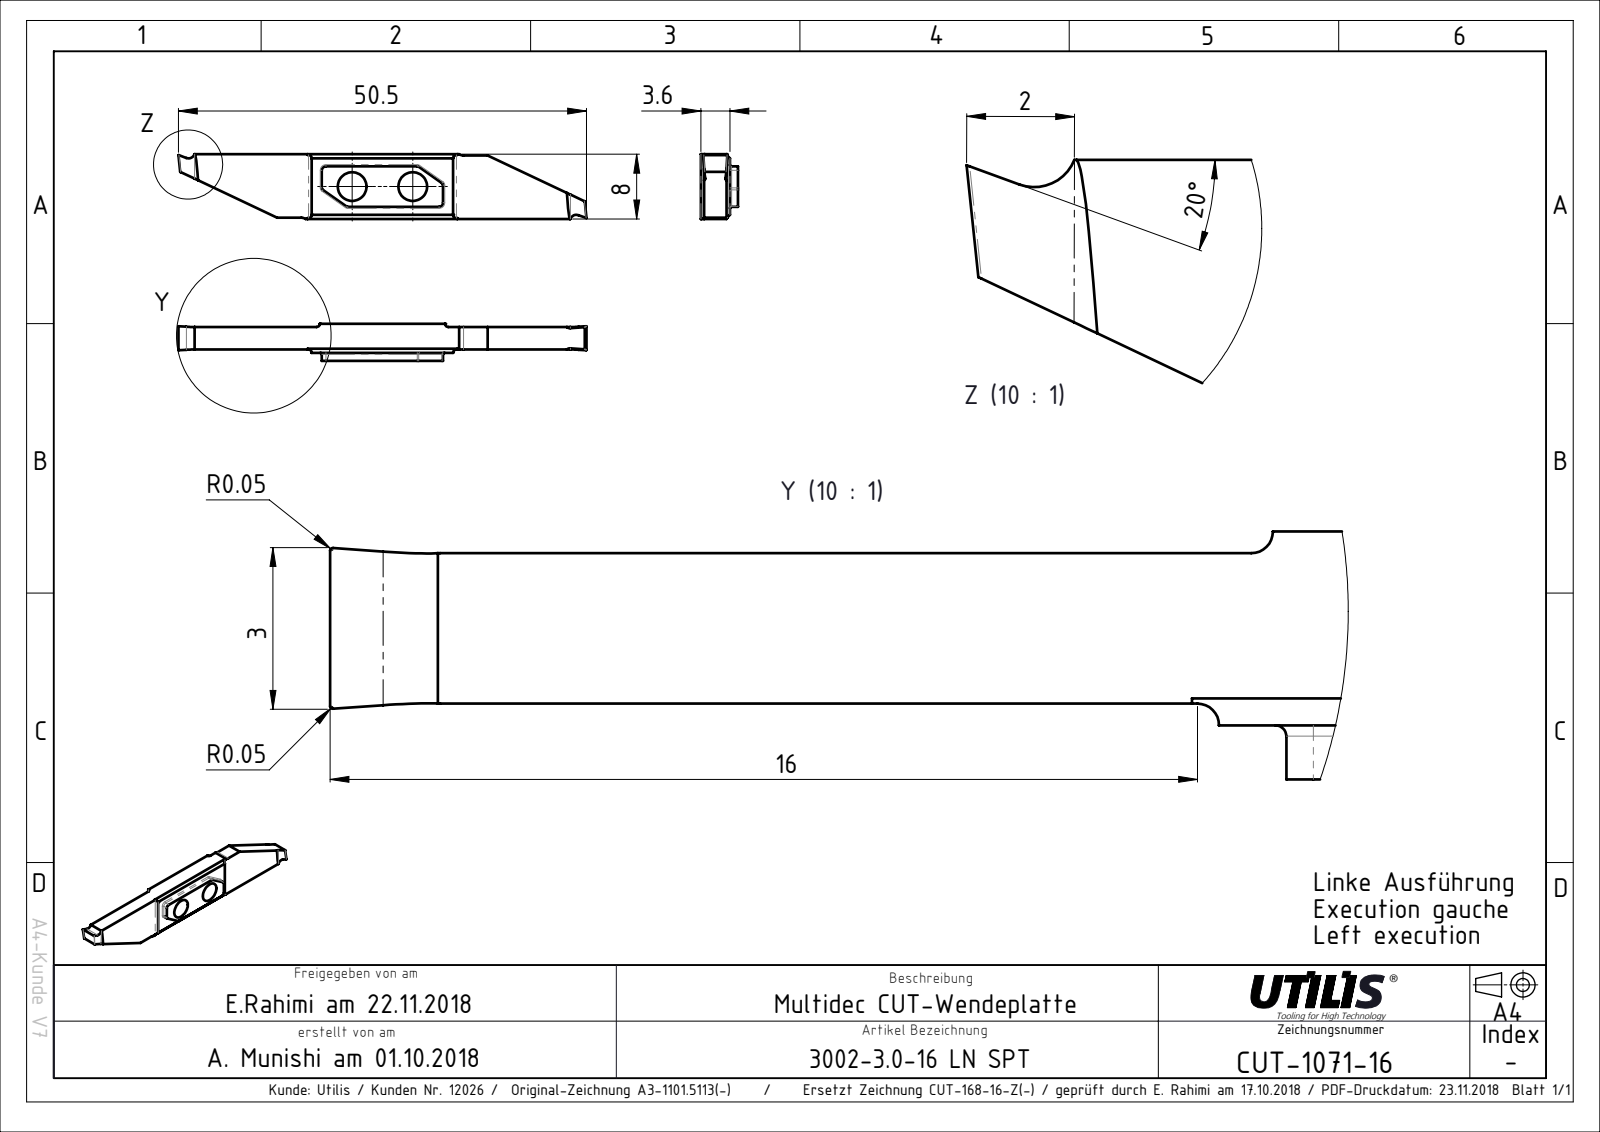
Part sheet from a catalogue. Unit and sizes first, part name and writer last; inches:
Units: inches
Overall size (bounding box): 1.988 × 0.315 × 0.142
Round holes (diameter × count): ⌀0.14 ×2
Partial cylindrical surfaces — rounded edges, fillets, slot ends (radius × count): R0.016 ×4, R0.039 ×2
Main face-to-face distances: 0.016, 0.126, 0.11, 0.142, 0.315, 0.712, 0.309, 0.015, 0.303, 1.988
Hole centre spacings: 0.295
Volume: 0.058 in³ · Surface area: 1.587 in²
Bodies: 1 solid, 42 faces (28 planar, 14 cylindrical, 0 other)
Part name (STEP PRODUCT): CUT-1071; ASME Y14.5
STEP written by: FormatWorks Professional (AP242_MANAGED_MODEL_BASED_3D_ENGINEERING_MIM_LF)
